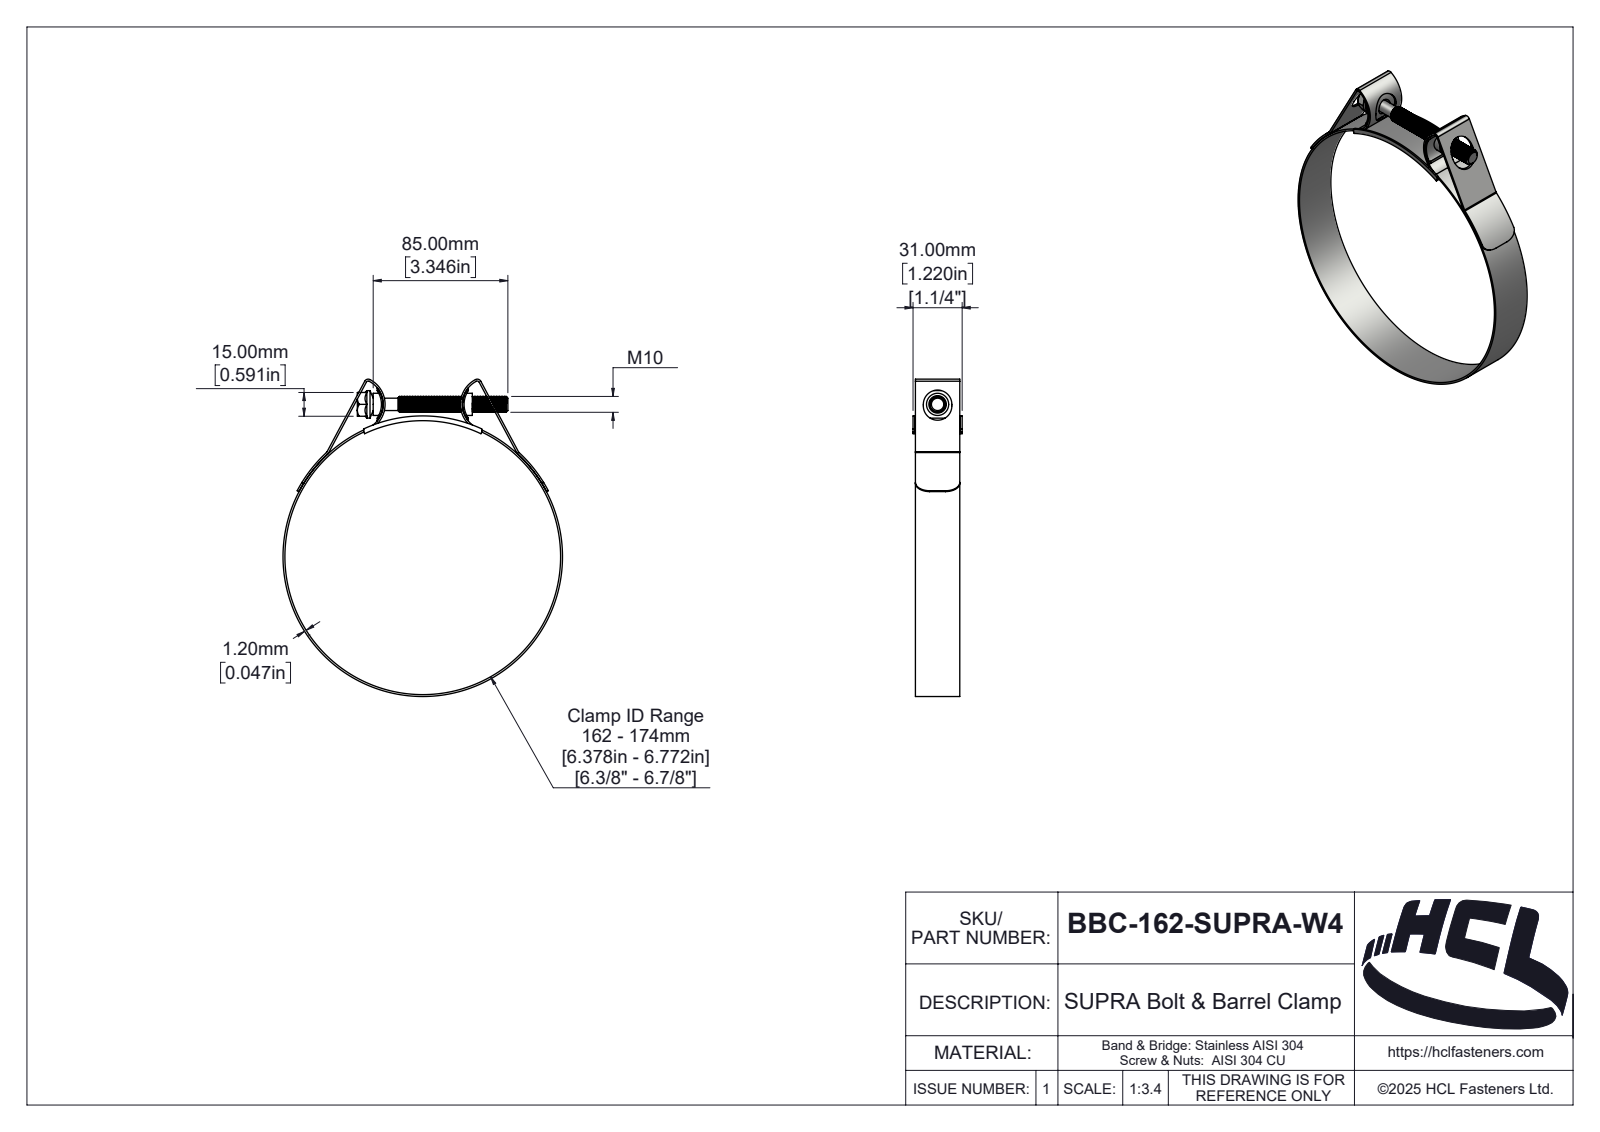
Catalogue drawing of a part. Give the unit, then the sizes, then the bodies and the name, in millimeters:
Units: millimetres
Overall size (bounding box): 200.2 × 176.4 × 31
Round holes (diameter × count): ⌀174 ×1
Round bosses / shafts (diameter × count): ⌀176.4 ×1, ⌀17.32 ×1, ⌀14 ×1, ⌀10 ×1, ⌀7.8 ×1
Partial cylindrical surfaces — rounded edges, fillets, slot ends (radius × count): R1 ×4, R1.3 ×2, R2 ×2, R2.5 ×2, R3.2 ×2, R9 ×2, R15.32 ×2, R16.32 ×2
Main face-to-face distances: 1.2, 28, 1.5, 29.5, 29.8, 28.3, 31, 28.6, 15, 2.5
Volume: 35 253 mm³ · Surface area: 53 324 mm²
Bodies: 5 solids, 379 faces (46 planar, 247 cylindrical, 86 other)
Part name (STEP PRODUCT): BBC-162-SUPRA-W4
STEP written by: SolidWorks 2025 (AUTOMOTIVE_DESIGN)
